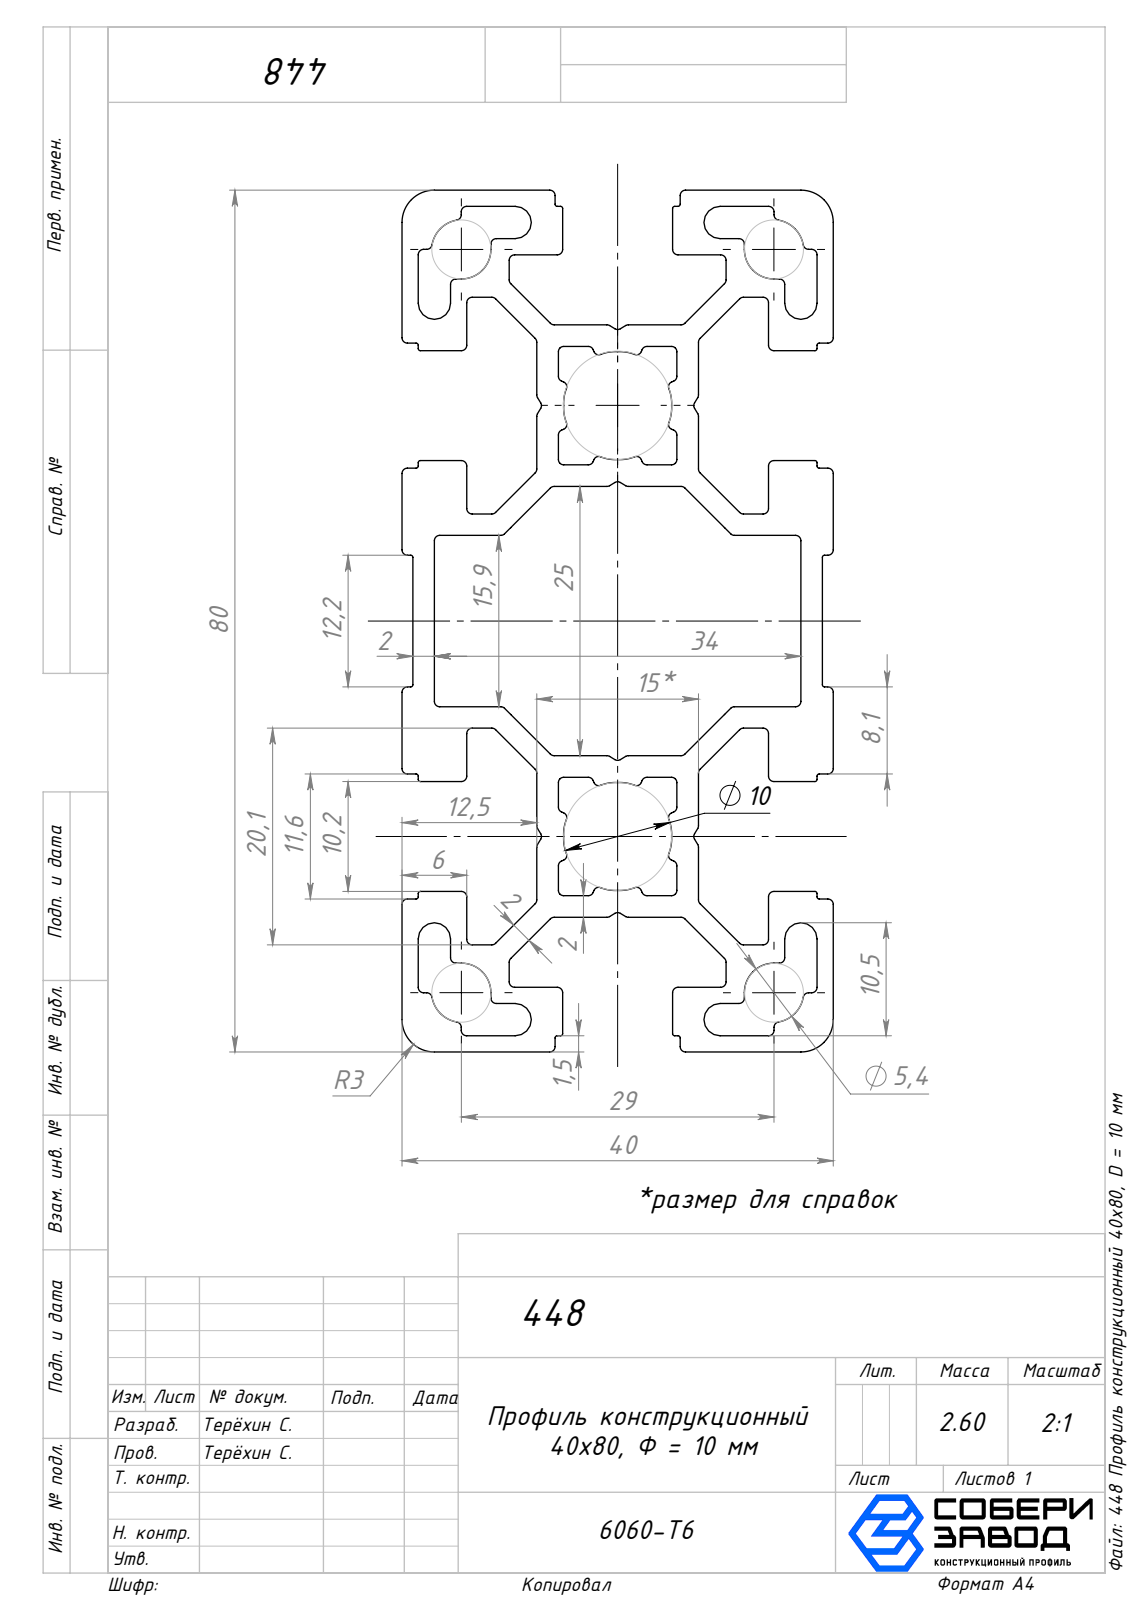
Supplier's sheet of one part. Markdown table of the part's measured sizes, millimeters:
| quantity | value |
| --- | --- |
| part name | 448 Профиль конструкционный 40х80, Ф = 10 мм_00; 448 Профиль конструкционный 40х80, Ф = 10 мм |
| STEP written by | SolidWorks 2025 (CONFIG_CONTROL_DESIGN) |
| units | millimeters |
| bodies | 1 solid, 482 faces (202 planar, 280 cylindrical, 0 other) |
| overall size | 1000 × 79.99 × 40 |
| volume | 964 336 mm³ |
| surface area | 814 283 mm² |
| partial cylindrical surfaces (radius × count) | 0.51 × 48, 0.2 × 24, 0.48 × 16, 0.48 × 16, 0.48 × 16, 0.49 × 16, 0.51 × 16, 0.54 × 16 |
| main face-to-face distances | 1.5, 12.5, 27.5, 6.01, 6.49, 21.49, 2.4, 12.6, 1.99, 39.99 |
